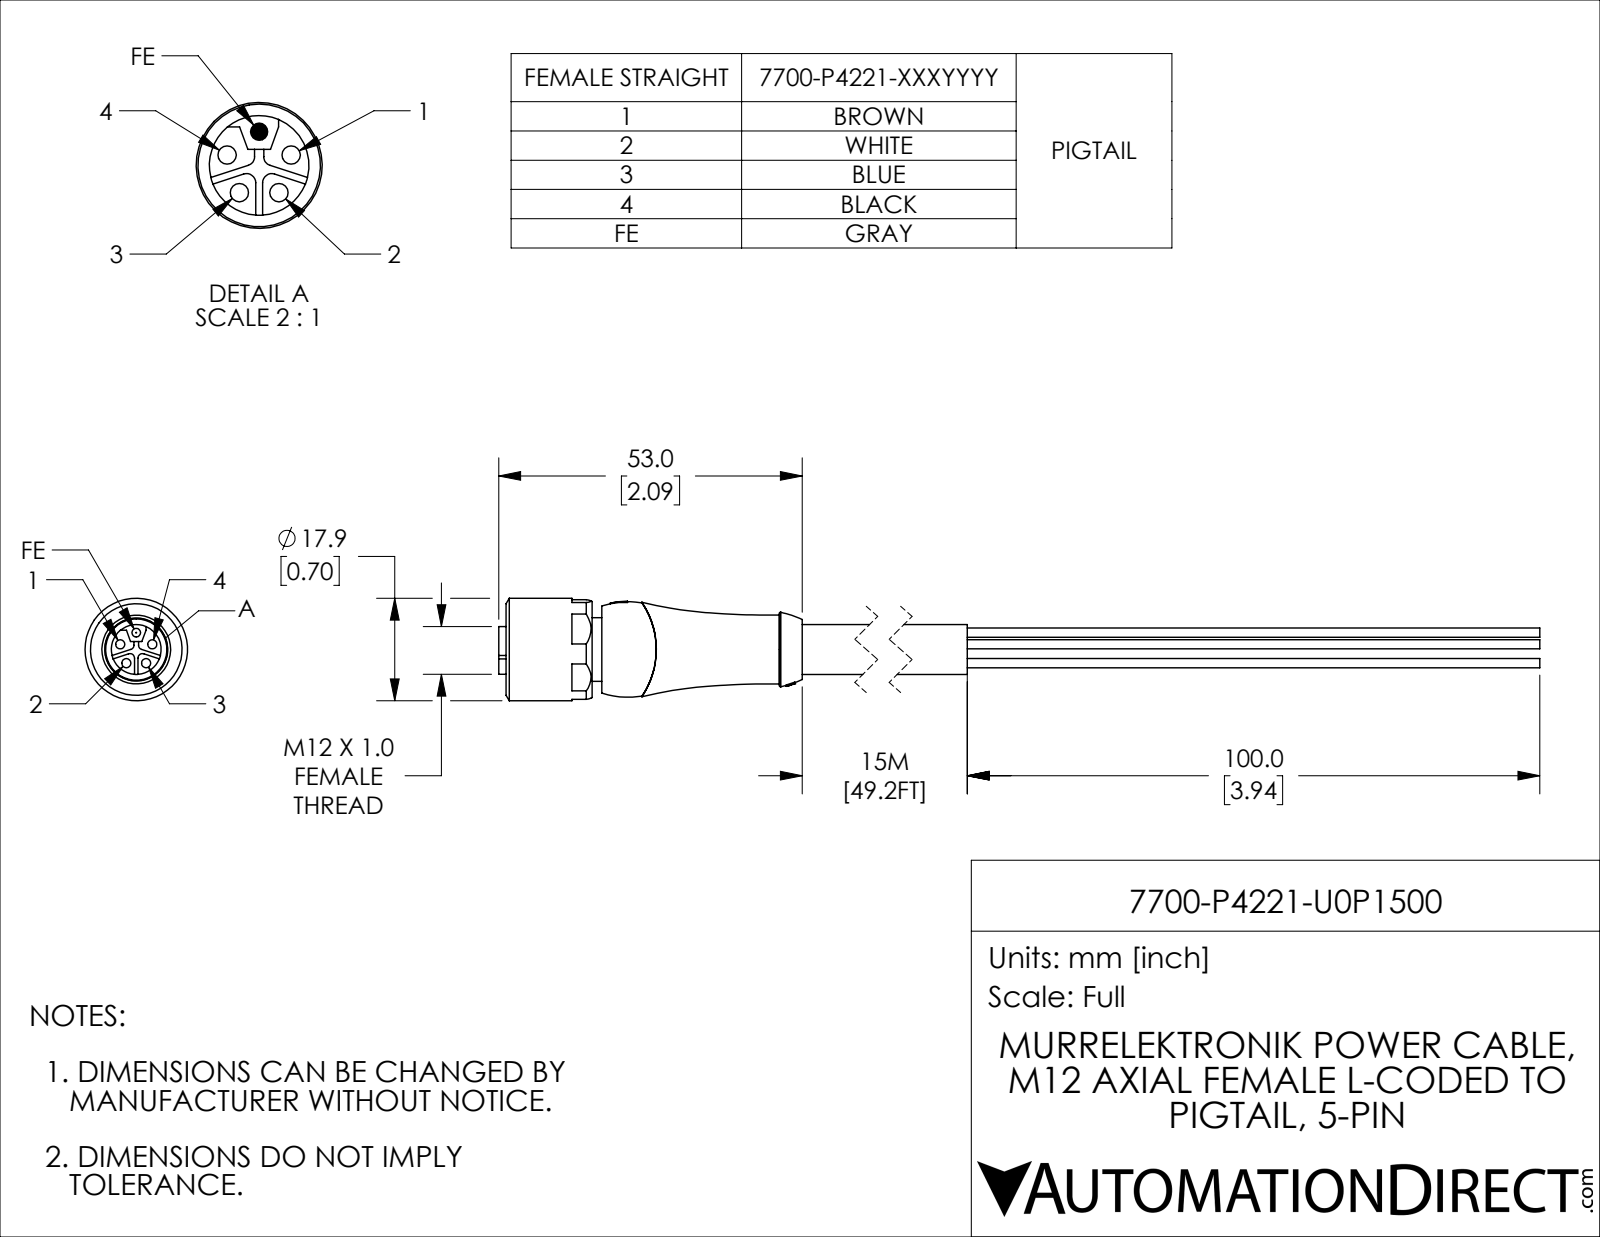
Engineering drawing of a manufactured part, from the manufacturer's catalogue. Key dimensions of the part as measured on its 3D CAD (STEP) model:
Part name (STEP PRODUCT): 7700-P4221-U0P1500
STEP written by: SolidWorks 2021 (CONFIG_CONTROL_DESIGN)
Units: inches
Bodies: 2 solids, 142 faces (69 planar, 40 cylindrical, 33 other)
Overall size (bounding box): 7.598 × 0.705 × 0.705
Volume: 0.735 in³ · Surface area: 12.83 in²
Round holes (diameter × count): ⌀0.063 ×4, ⌀0.433 ×1, ⌀0.512 ×1
Round bosses / shafts (diameter × count): ⌀0.705 ×1, ⌀0.51 ×1, ⌀0.437 ×1, ⌀0.343 ×1, ⌀0.063 ×1, ⌀0.059 ×1
Partial cylindrical surfaces — rounded edges, fillets, slot ends (radius × count): R0.031 ×4
Main face-to-face distances: 0.657, 0.591, 0.067, 0.667, 3.61, 3.02, 2.953, 0.181, 0.362, 0.228
Hole centre spacings: 0.116, 0.136, 0.22
